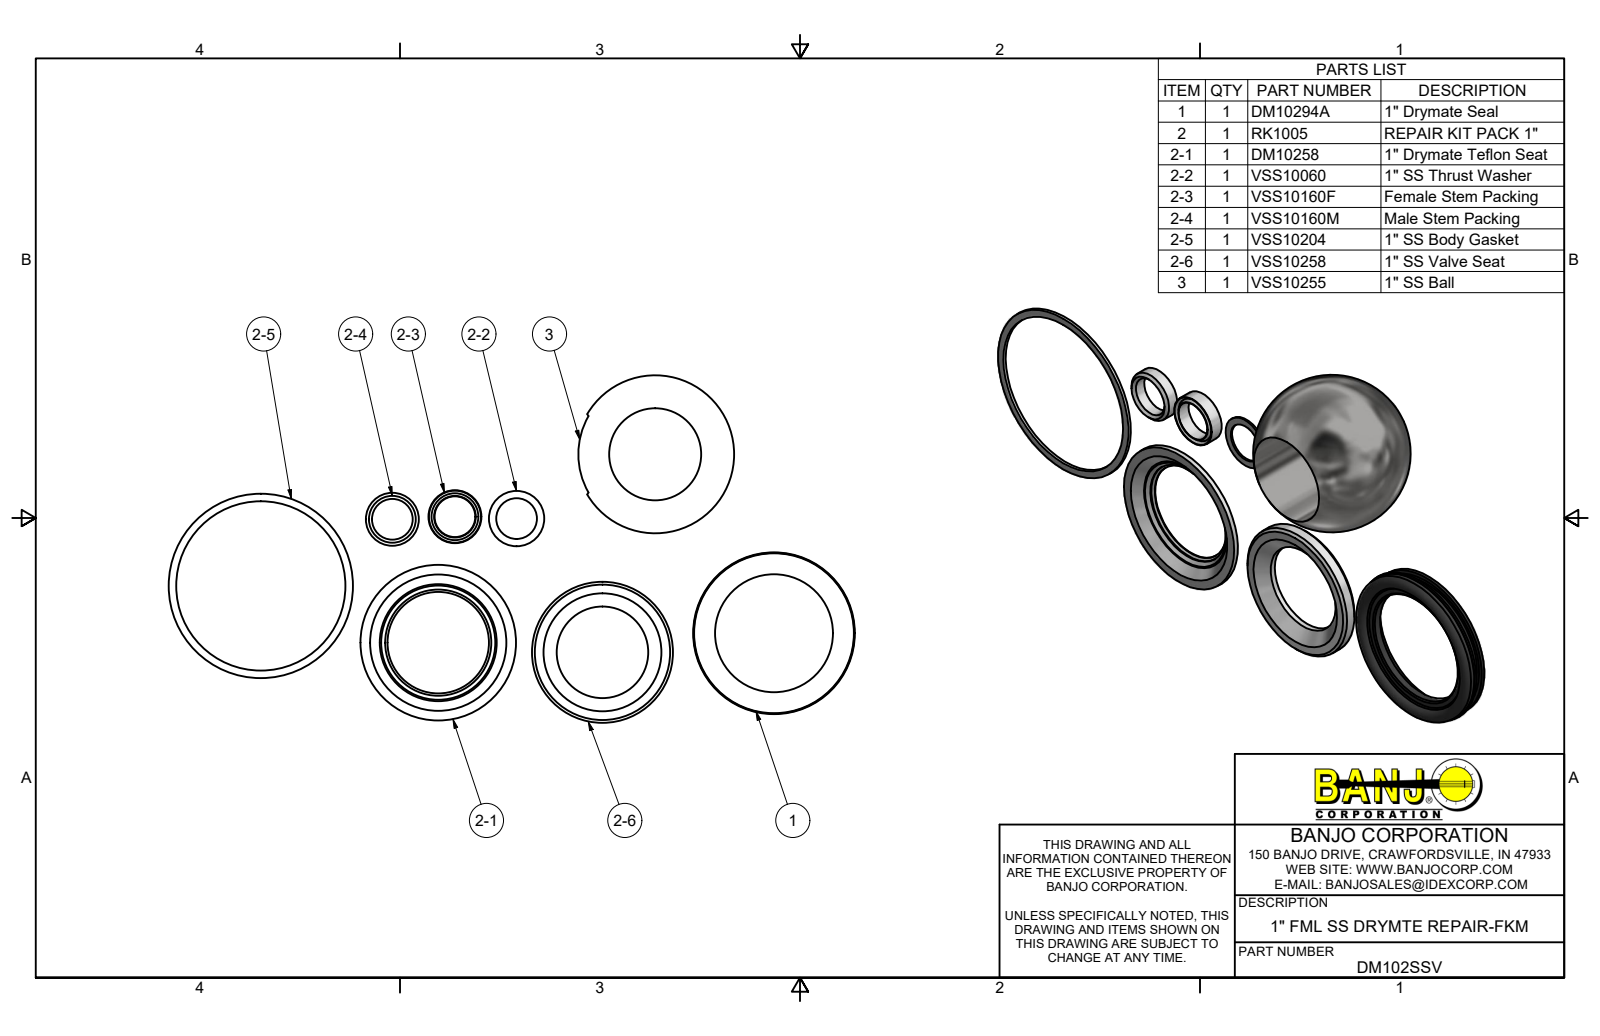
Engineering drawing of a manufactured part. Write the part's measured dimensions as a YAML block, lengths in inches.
part_name: "DM102SSV; RK1005; DM10258; VSS10060 (+6 more)"
step_written_by: "Autodesk Inventor 2019 (AUTOMOTIVE_DESIGN)"
units: inches
bodies: {solids: 8, faces: 60, planar: 22, cylindrical: 19, other: 19}
overall_size: [7.292, 3.689, 1.358]
volume: 1.699
surface_area: 26.5
round_holes:
  - {diameter: 0.432, count: 2}
  - {diameter: 0.434, count: 1}
  - {diameter: 0.975, count: 1}
  - {diameter: 0.98, count: 1}
  - {diameter: 1.076, count: 1}
  - {diameter: 1.13, count: 1}
  - {diameter: 1.253, count: 1}
  - {diameter: 1.597, count: 1}
  - {diameter: 1.8, count: 1}
round_bosses_or_shafts:
  - {diameter: 0.564, count: 2}
  - {diameter: 1.96, count: 1}
  - {diameter: 1.72, count: 1}
  - {diameter: 1.679, count: 1}
  - {diameter: 1.653, count: 1}
  - {diameter: 1.496, count: 1}
  - {diameter: 0.589, count: 1}
partial_cylinders:
  - {radius: 0.75, count: 1}
face_to_face_distances: [0.14, 0.181, 0.041, 0.035, 0.105, 0.146, 0.145, 0.015, 0.18, 0.04]
hole_center_spacings: [0.654, 0.667, 1.32, 1.35, 1.398, 1.558, 1.567, 1.623]
